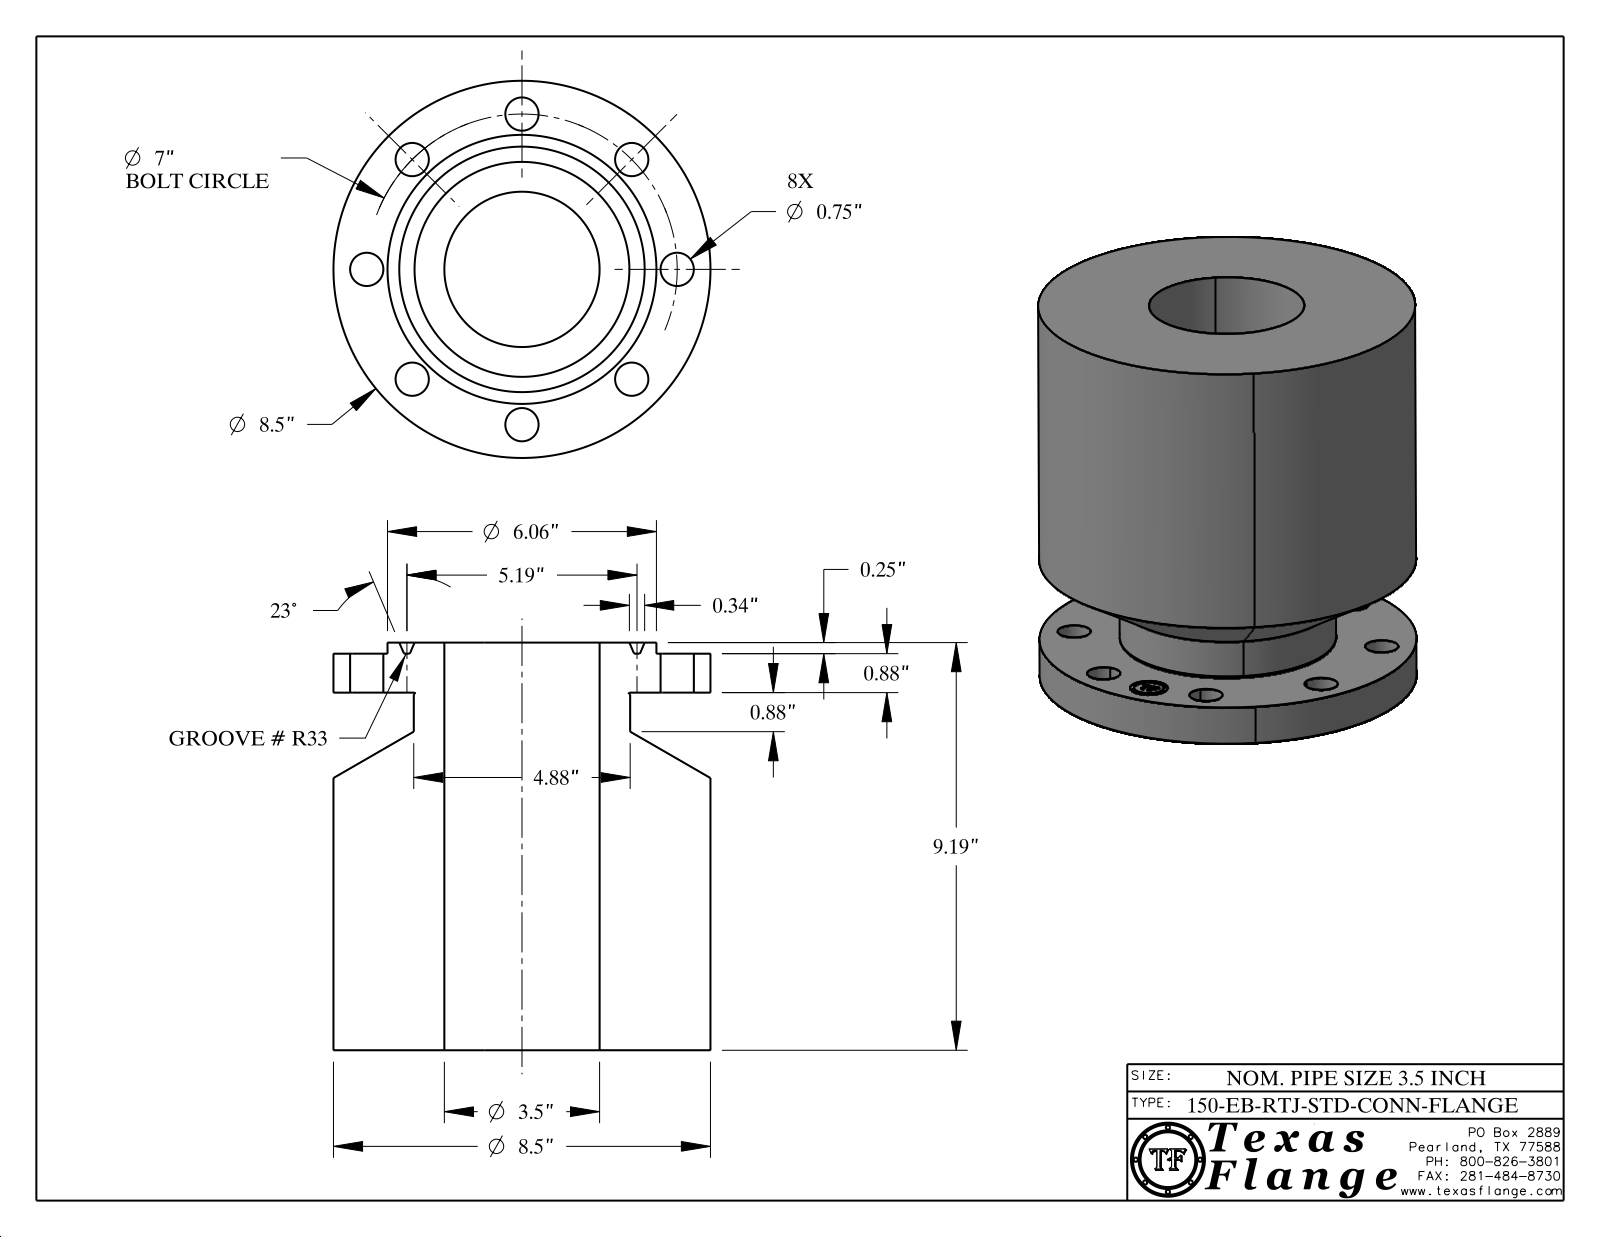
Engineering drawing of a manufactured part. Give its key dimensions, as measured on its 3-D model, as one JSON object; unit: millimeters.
{"part_name": "3.5-150-EB-RTJ-STD-CONN-FLANGE", "step_written_by": "CATIA V5 STEP AP214 (AUTOMOTIVE_DESIGN)", "units": "millimeters", "bodies": {"solids": 1, "faces": 431, "planar": 371, "cylindrical": 46, "other": 14}, "overall_size": [233.4, 215.9, 215.9], "volume_mm3": 6011000, "surface_area_mm2": 321400, "round_holes": [[19.1, 8], [21.6, 1], [88.9, 1]], "round_bosses_or_shafts": [[1.3, 8], [215.9, 1], [154, 1], [124, 1], [17, 1]], "face_to_face_distances": [204.7, 22.3, 227, 6.4, 28.7, 233.3, 28.5, 22.1, 204.9, 6.5], "hole_center_spacings": [88.9, 68, 125.7, 164.3, 34.7, 98.8, 147.8, 174.4]}
